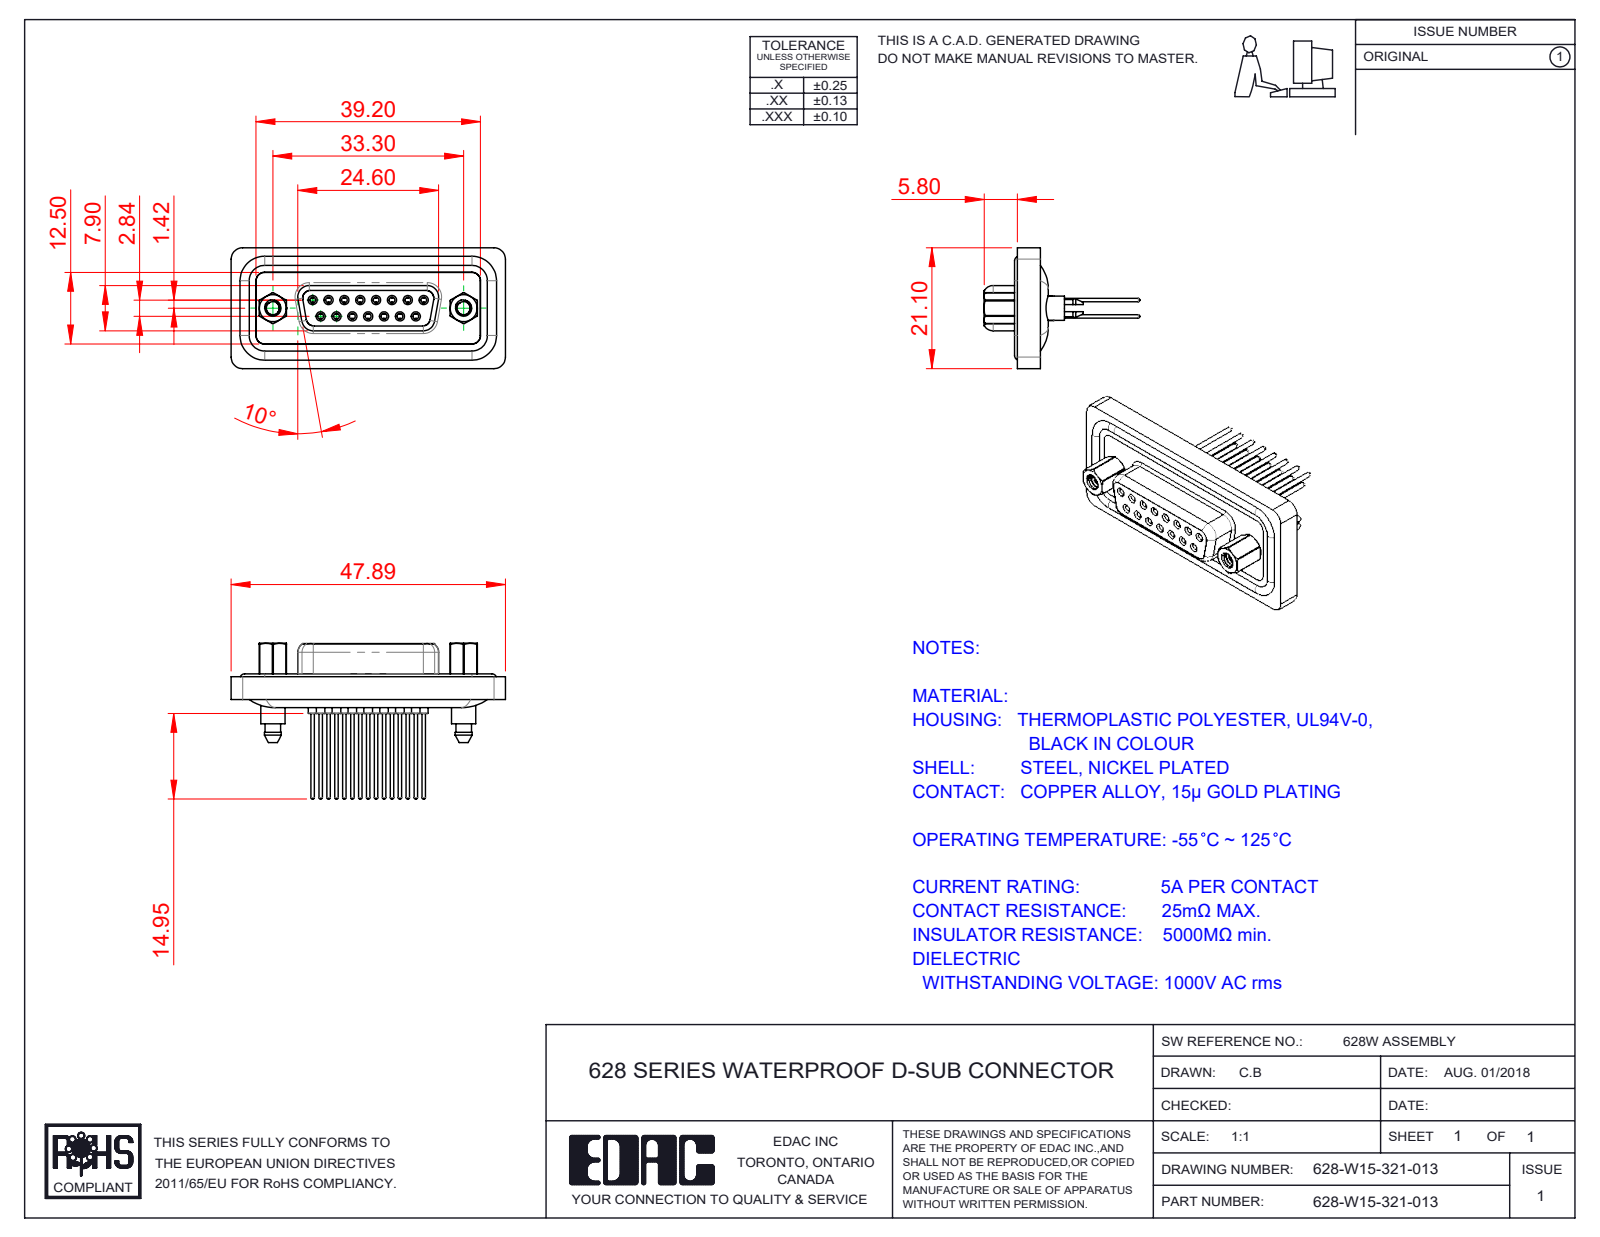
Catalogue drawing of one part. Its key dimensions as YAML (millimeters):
part_name: "628W Contact Row 2_21; 628W Shell Front_15 Contacts; 628W 4-40 Threaded Boardlock; 628-W15-321-013 (+4 more)"
step_written_by: "SolidWorks 2020 (CONFIG_CONTROL_DESIGN)"
units: millimeters
bodies: {solids: 23, faces: 1324, planar: 340, cylindrical: 563, other: 421}
overall_size: [47.89, 27.2, 21.1]
volume: 5651
surface_area: 9963
round_holes:
  - {diameter: 1, count: 15}
  - {diameter: 1.1, count: 15}
  - {diameter: 1.5, count: 15}
  - {diameter: 1.7, count: 15}
  - {diameter: 1.8, count: 15}
  - {diameter: 2, count: 15}
  - {diameter: 2.26, count: 2}
  - {diameter: 2.29, count: 2}
  - {diameter: 4, count: 2}
  - {diameter: 4.25, count: 2}
  - {diameter: 4.8, count: 2}
round_bosses_or_shafts:
  - {diameter: 1.6, count: 19}
  - {diameter: 2.2, count: 15}
  - {diameter: 1.5, count: 15}
  - {diameter: 0.6, count: 15}
  - {diameter: 5.4, count: 2}
  - {diameter: 4.9, count: 2}
  - {diameter: 2.79, count: 2}
  - {diameter: 4.8, count: 1}
partial_cylinders:
  - {radius: 1.5, count: 16}
  - {radius: 2, count: 16}
  - {radius: 1.35, count: 8}
  - {radius: 1.6, count: 6}
  - {radius: 0.5, count: 4}
  - {radius: 0.9, count: 4}
  - {radius: 1.75, count: 4}
  - {radius: 2.7, count: 4}
face_to_face_distances: [0.4, 1.8, 2.9, 2.5, 1.6, 1.1, 7.45, 13.65, 4.1, 4.5]
hole_center_spacings: [3.16, 2.77, 5.54, 8.31, 3.17, 3.15, 11.08, 5.03]
